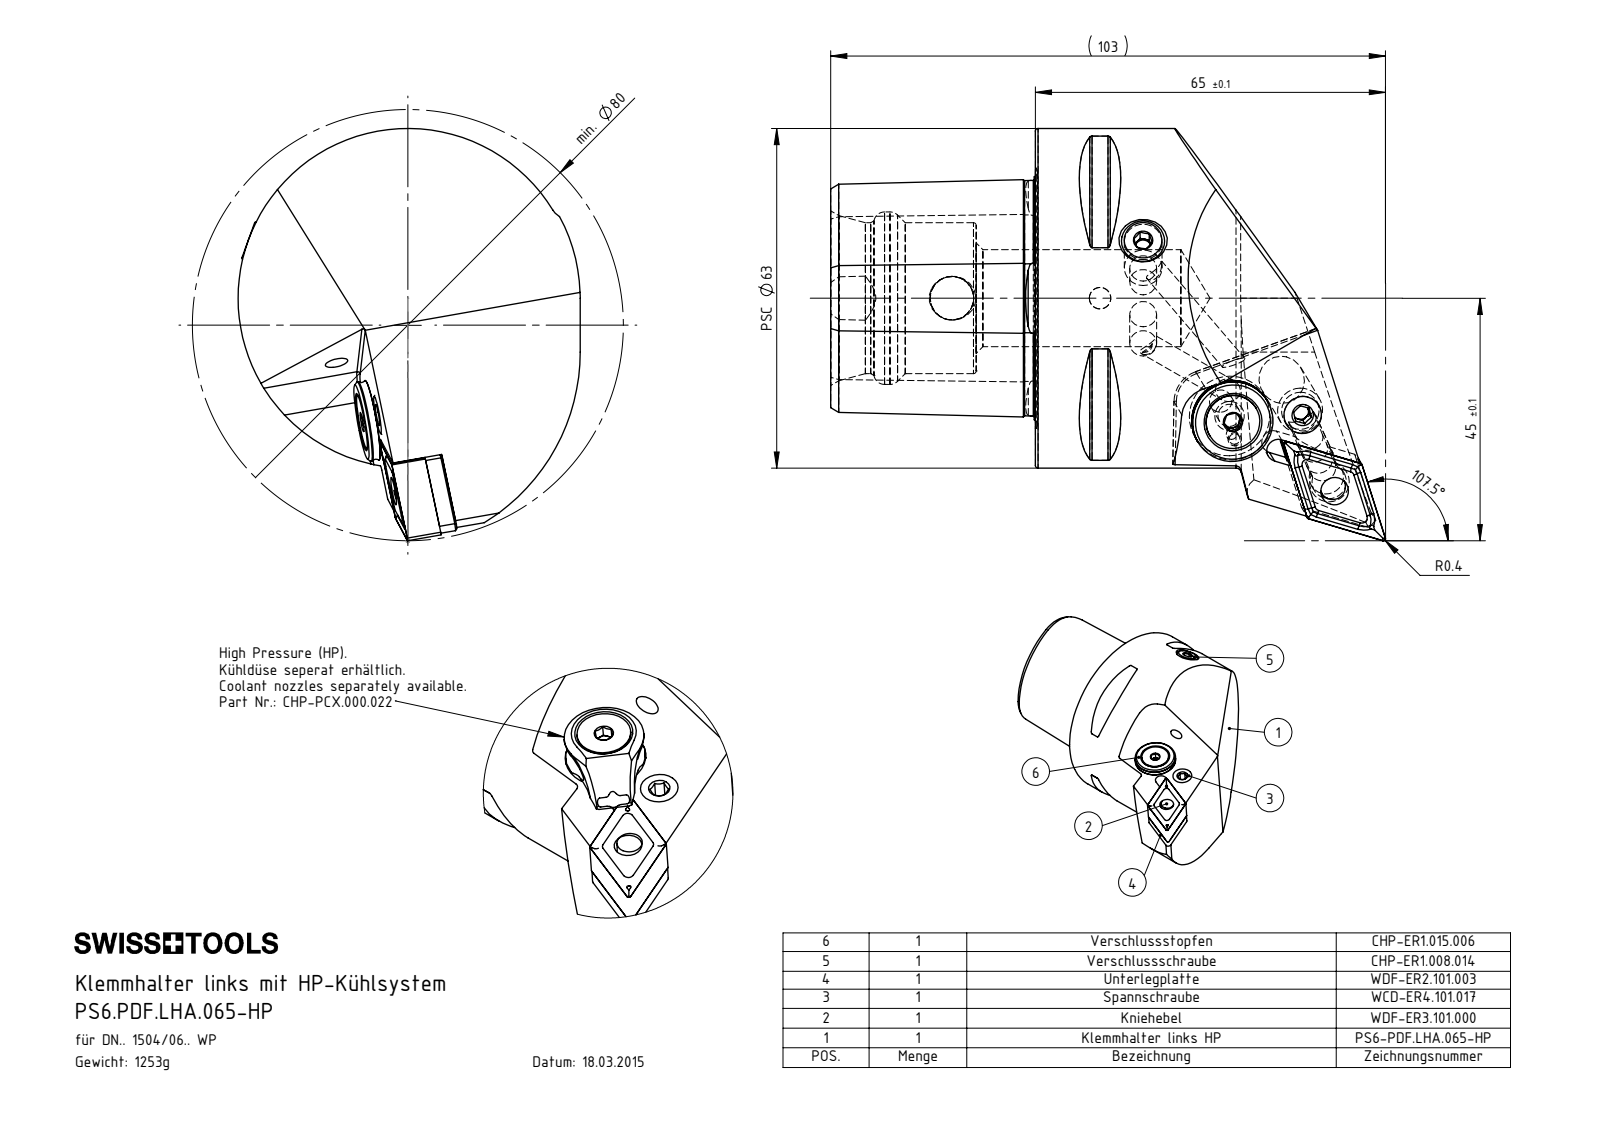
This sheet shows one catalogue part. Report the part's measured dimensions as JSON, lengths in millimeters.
{"part_name": "WDF-ER2.101.003_A; WCD-ER1.101.000; WDF-ER3.101.000_A; DIN 7991 - M5x15 (+8 more)", "step_written_by": "SolidWorks 2017 (AUTOMOTIVE_DESIGN)", "units": "millimeters", "bodies": {"solids": 11, "faces": 441, "planar": 130, "cylindrical": 113, "other": 198}, "overall_size": [103, 76.5, 63.5], "volume_mm3": 160343, "surface_area_mm2": 33596, "round_holes": [[4.2, 2], [5, 2], [7, 2], [1.2, 1], [2, 1], [2.5, 1], [3, 1], [4, 1], [5.16, 1], [5.2, 1], [6.4, 1], [8.1, 1]], "round_bosses_or_shafts": [[8, 2], [63, 1], [15, 1], [13.4, 1], [10, 1], [7.9, 1], [6.4, 1], [5.5, 1]], "partial_cylinders_radius": [[0.5, 10], [0.4, 4], [1, 4], [2.5, 3], [6, 2], [2.1, 1], [2.35, 1], [2.8, 1]], "face_to_face_distances": [38, 6.03, 24.88, 12.7, 1.53, 4.5, 27, 11, 12.41, 55.8], "hole_center_spacings": [23.5, 4.51, 20.38, 20.39, 4.5, 4.52, 13.21, 13.22]}
